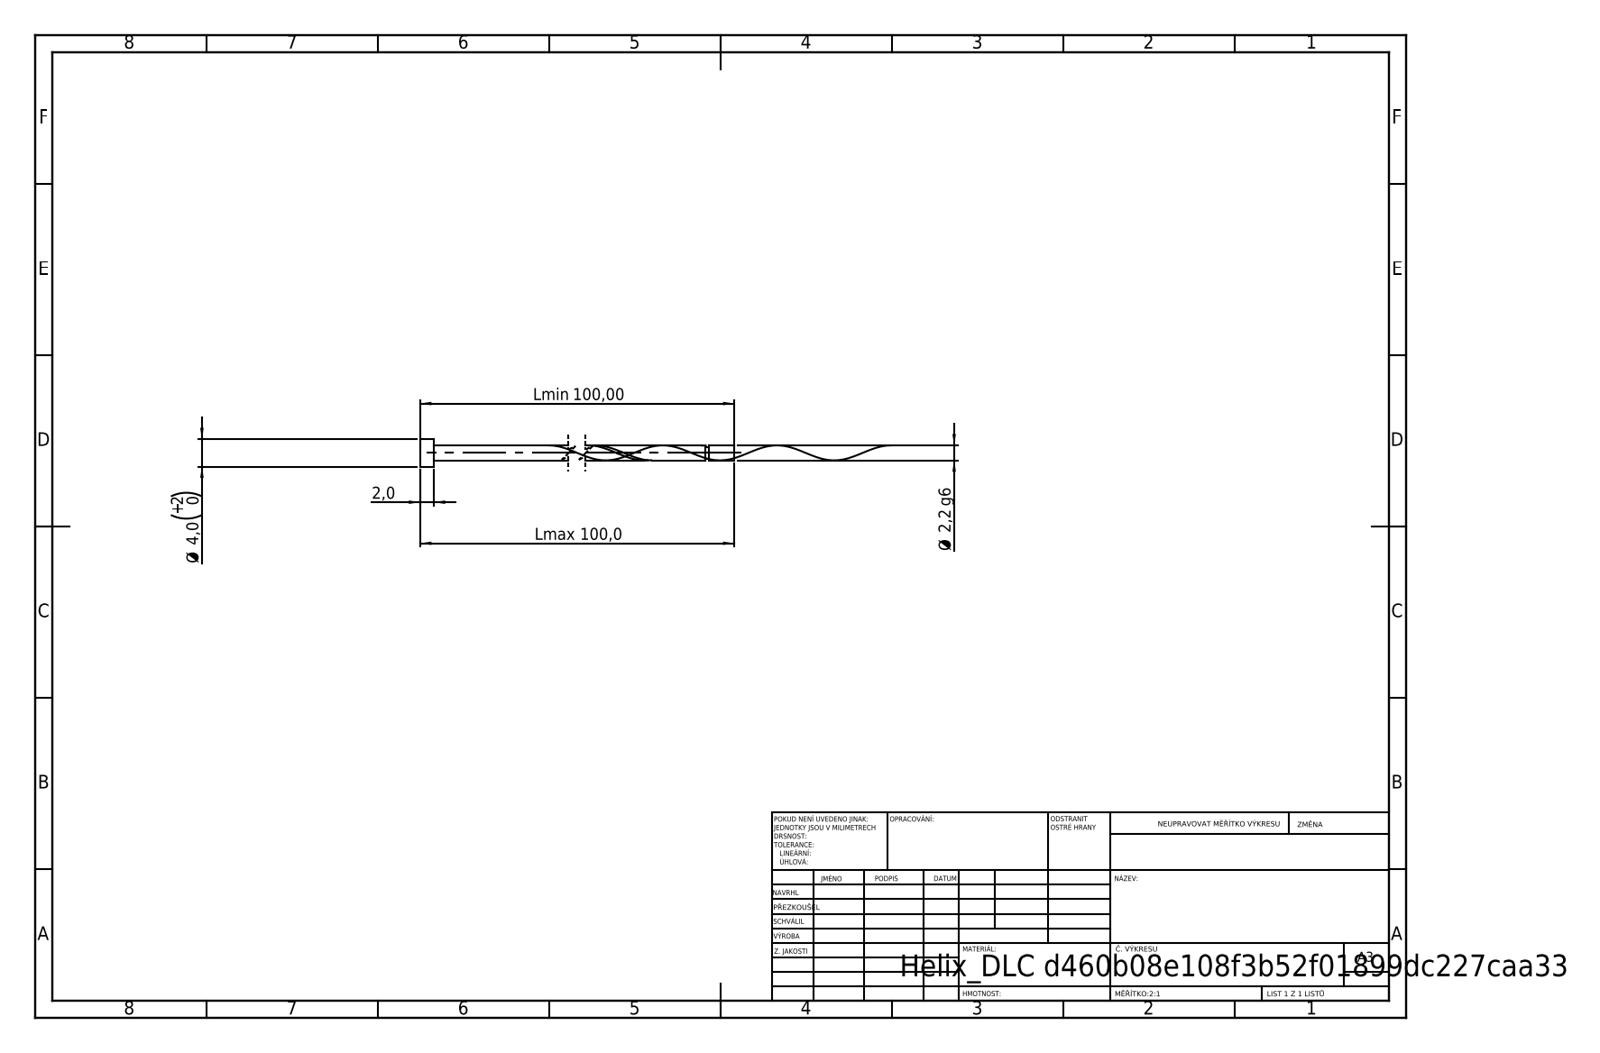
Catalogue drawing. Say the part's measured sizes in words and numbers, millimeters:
Its 3-D file was written by "SolidWorks 2019 (CONFIG_CONTROL_DESIGN)". It is 1 solid with 21 faces: 6 planar, 14 cylindrical and 1 other. Overall it measures 100 by 4 by 4 millimeters. Its volume is 393 cubic millimeters and its surface area 741 square millimeters. Round bosses or shafts: 1 of diameter 4, 1 of diameter 2.2, 1 of diameter 1.76. The main face-to-face distances are 2, 100, 98, 96.26, 94.26, 3.74, 95.82, 93.82, 0.44, 4.18.
